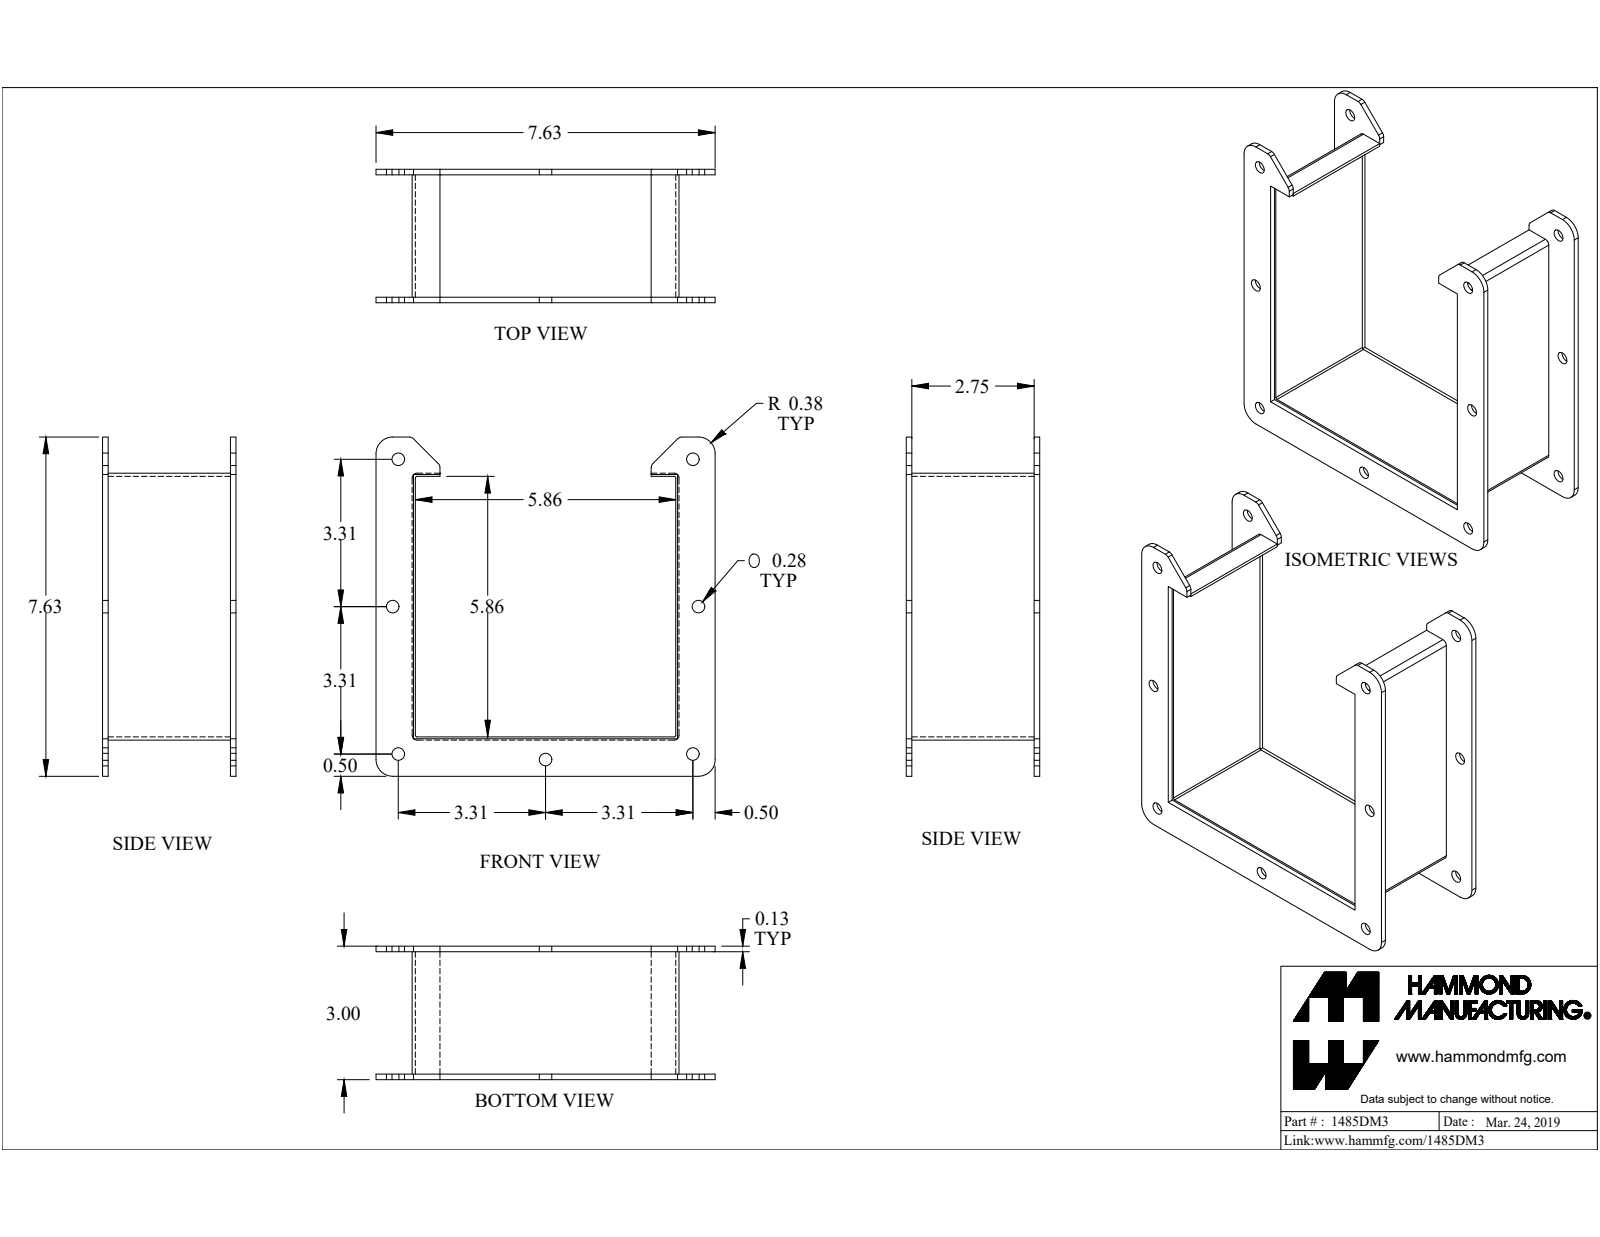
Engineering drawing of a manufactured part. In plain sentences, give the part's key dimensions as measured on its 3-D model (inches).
The part is named "1485DM3". Its 3-D file was written by "SolidWorks 2019 (CONFIG_CONTROL_DESIGN)". It is 3 solids with 84 faces: 46 planar, 38 cylindrical and 0 other. Overall it measures 7.625 by 7.625 by 3 inches. Its volume is 8.206 cubic inches and its surface area 191.1 square inches. Round holes: 7 of diameter 0.281. Partial cylindrical surfaces (rounded edges, fillets, slot ends): 4 of radius 0.036, 4 of radius 0.108, 4 of radius 0.125, 4 of radius 0.375. The main face-to-face distances are 0.072, 5.928, 0.125, 2.875, 6, 5.856, 2.75, 2.875, 0.125, 3. The hole center spacings are 7.519, 6.625, 3.315, 3.315, 9.369, 4.861, 4.862, 6.875.
